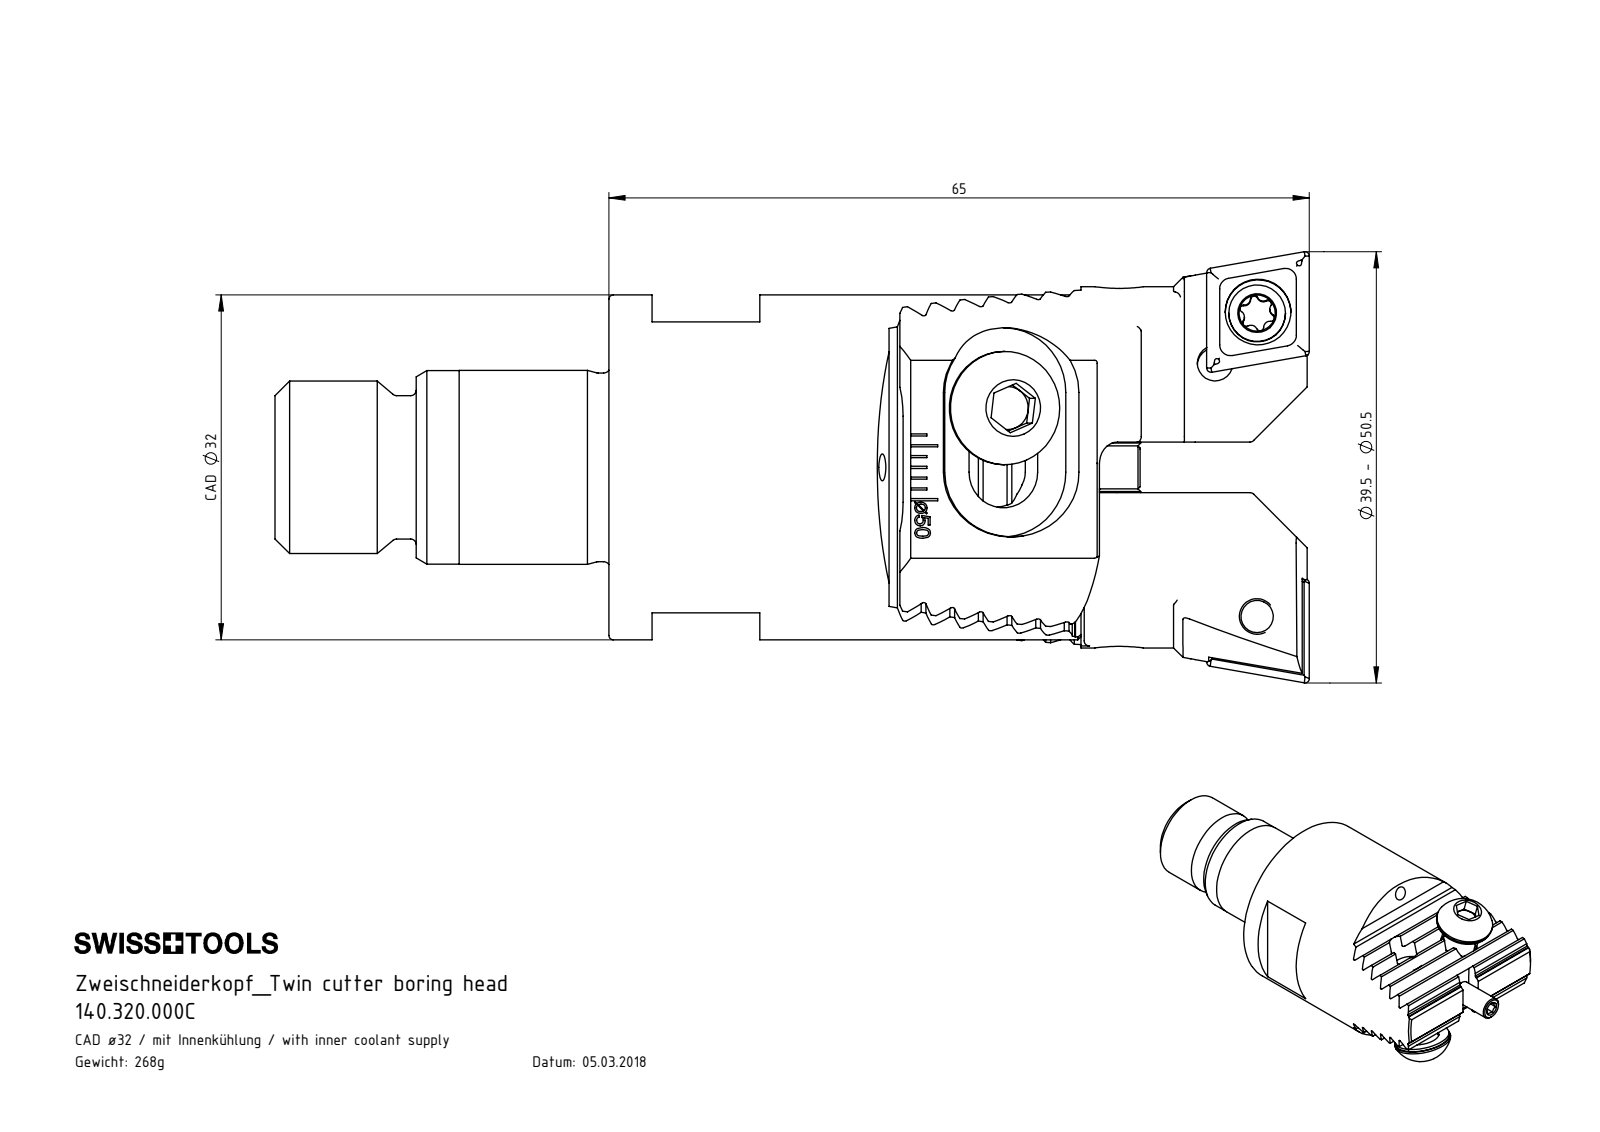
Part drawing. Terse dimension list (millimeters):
name: Z20-ER2.001.013_A; CA3-Z32.K21.065_B; 140.320.000C; Z32-ER1.002.016_A (+2 more)
written by: SolidWorks 2017 (CONFIG_CONTROL_DESIGN)
unit: mm
bodies: 6 solids, 315 faces (147 planar, 96 cylindrical, 72 other)
size: 80.3 × 32 × 32
volume: 34 201 mm³; area: 10 540 mm²
holes: 4× ⌀2.5, 2× ⌀5, 2× ⌀6.4, 2× ⌀6.8, 1× ⌀2, 1× ⌀3
bosses: 2× ⌀10.5, 2× ⌀10.2, 2× ⌀6, 1× ⌀32, 1× ⌀18, 1× ⌀17.95, 1× ⌀17.5, 1× ⌀16
rounds: 14× R0.2, 2× R220
face distances: 2.38, 4.76, 7.14, 9.52, 27, 11.9, 43.8, 31, 74.8, 3.77
